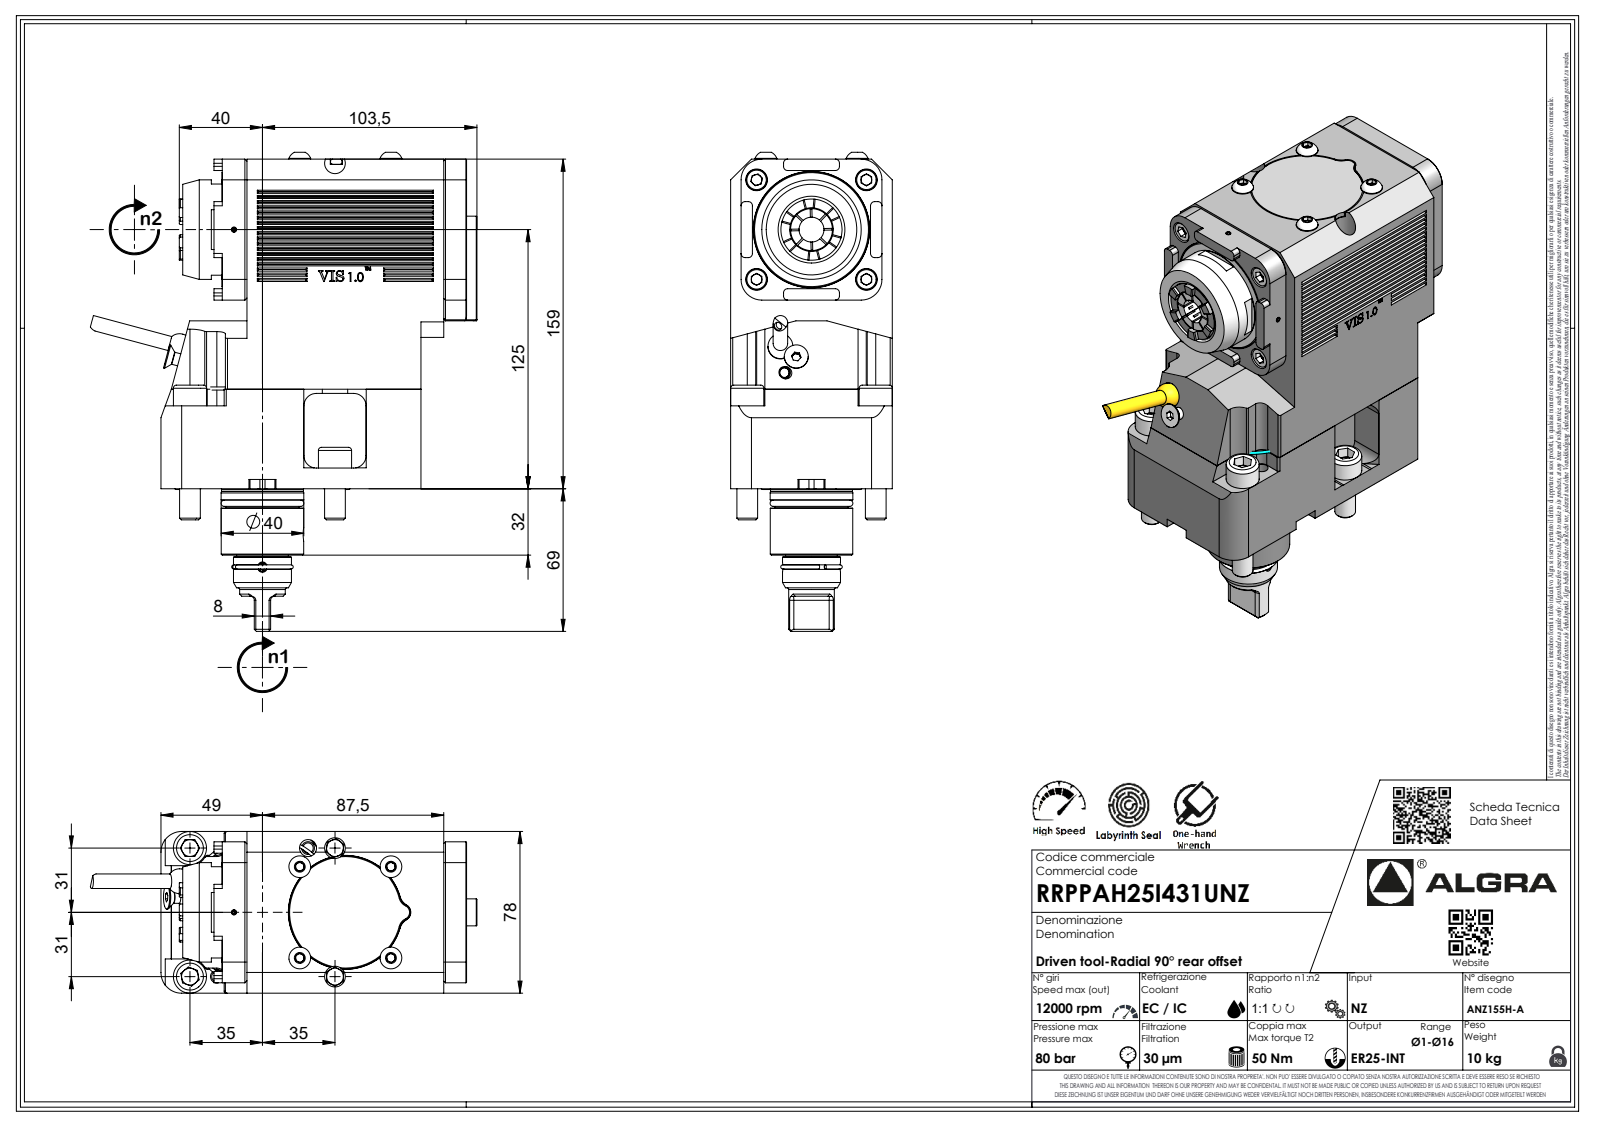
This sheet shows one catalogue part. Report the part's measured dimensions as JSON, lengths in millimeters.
{"part_name": "RRPPAH25I431UNZ", "step_written_by": "SolidWorks 2023 (AUTOMOTIVE_DESIGN)", "units": "millimeters", "bodies": {"solids": 1, "faces": 551, "planar": 347, "cylindrical": 96, "other": 108}, "overall_size": [227.8, 186.57, 78], "volume_mm3": 1515000, "surface_area_mm2": 99310, "round_holes": [[2.1, 1], [4, 1]], "round_bosses_or_shafts": [[10, 4], [16, 2], [48, 1], [39.9, 1], [39.8, 1], [39.5, 1], [35.1, 1], [28, 1]], "partial_cylinders_radius": [[2, 23], [1, 8], [10, 8], [0.33, 7], [0.52, 7], [3.7, 7], [3.5, 2], [4.1, 2]], "face_to_face_distances": [78, 159, 11, 22, 5, 73, 106, 68, 125.5, 136.5]}
